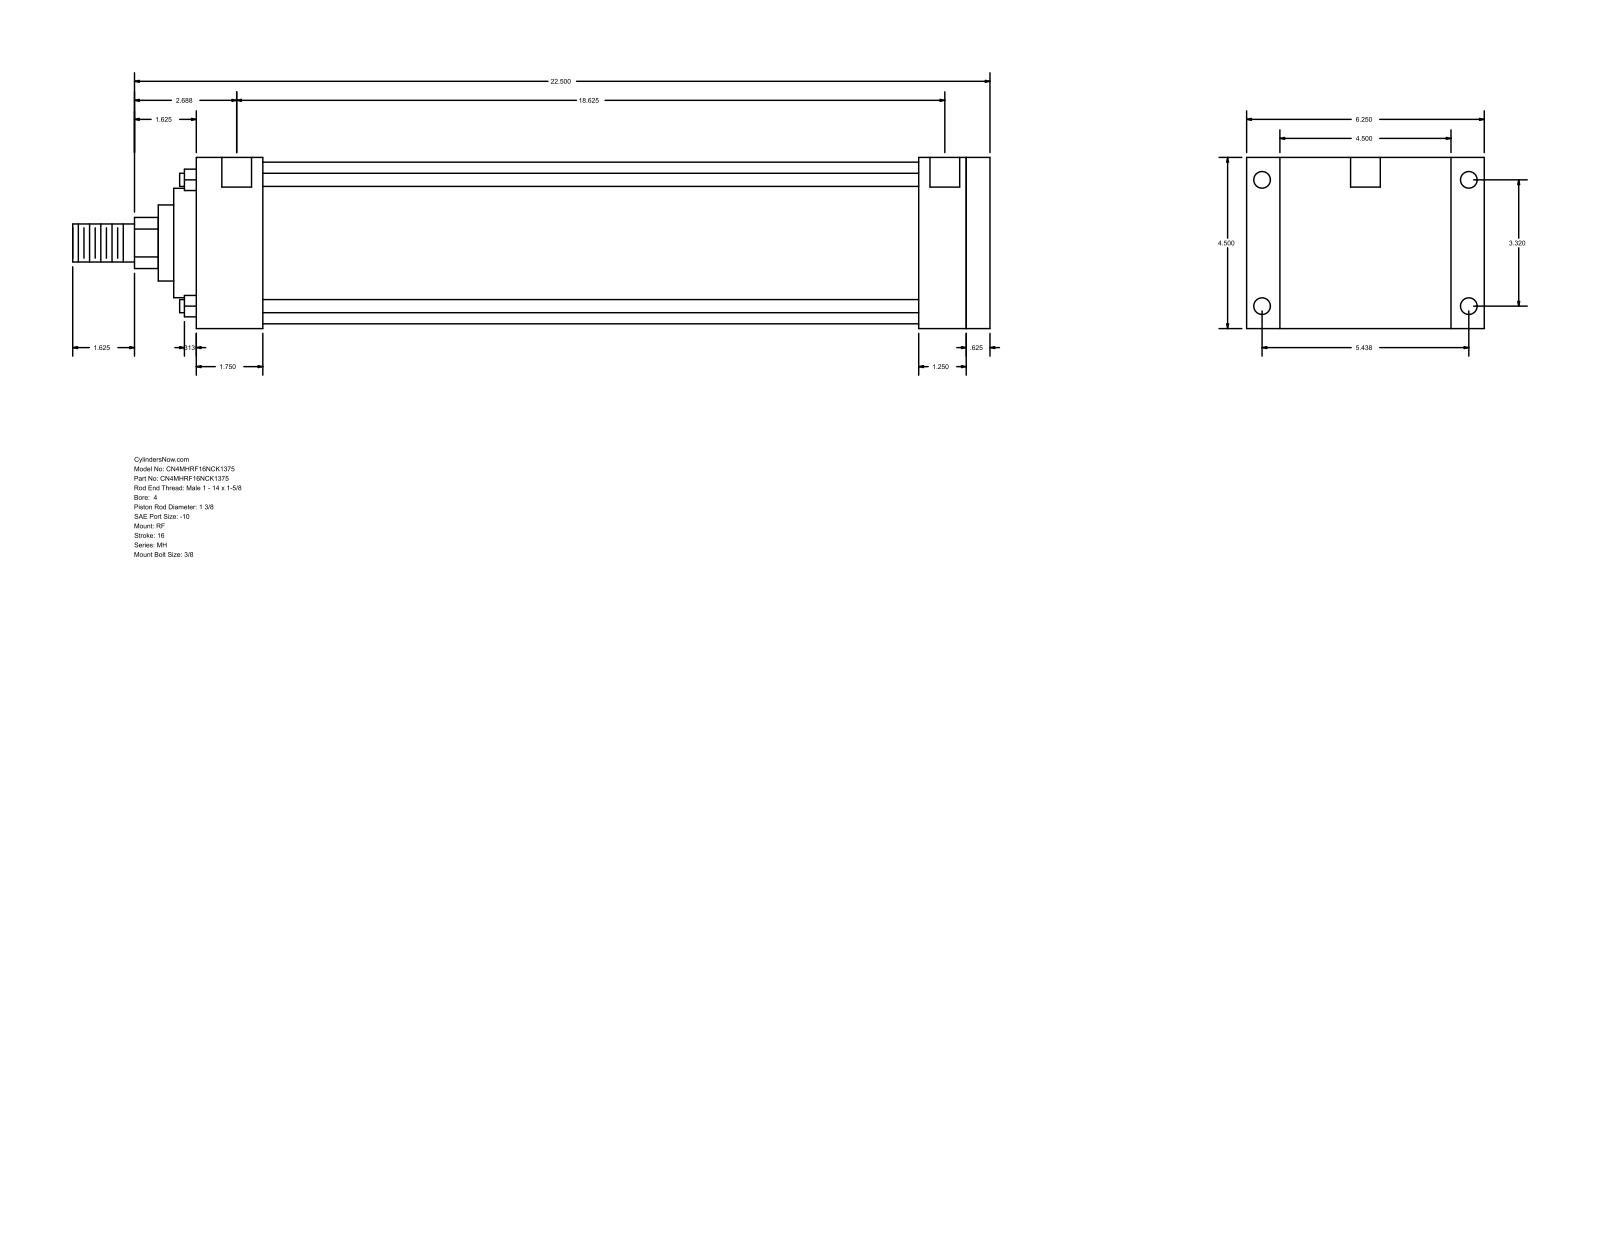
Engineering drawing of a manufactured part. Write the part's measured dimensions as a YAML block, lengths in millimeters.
part_name: "MH_RF__0400_1.375"
step_written_by: "GSSL Pune (CONFIG_CONTROL_DESIGN)"
units: millimeters
bodies: {solids: 0, faces: 94, planar: 65, cylindrical: 29, other: 0}
overall_size: [612.77, 158.75, 114.3]
round_holes:
  - {diameter: 8.73, count: 4}
  - {diameter: 11.13, count: 4}
  - {diameter: 19.84, count: 2}
round_bosses_or_shafts:
  - {diameter: 8.76, count: 4}
  - {diameter: 107.95, count: 1}
  - {diameter: 73.03, count: 1}
  - {diameter: 50.8, count: 1}
  - {diameter: 34.92, count: 1}
  - {diameter: 25.4, count: 1}
partial_cylinders:
  - {radius: 17.06, count: 1}
face_to_face_distances: [114.3, 530.23, 15.88, 514.35, 44.45, 469.9, 485.78, 482.61, 438.16, 31.74]
hole_center_spacings: [84.32, 138.12, 161.82, 476.25, 1.58, 1.59, 473.08, 474.66]
